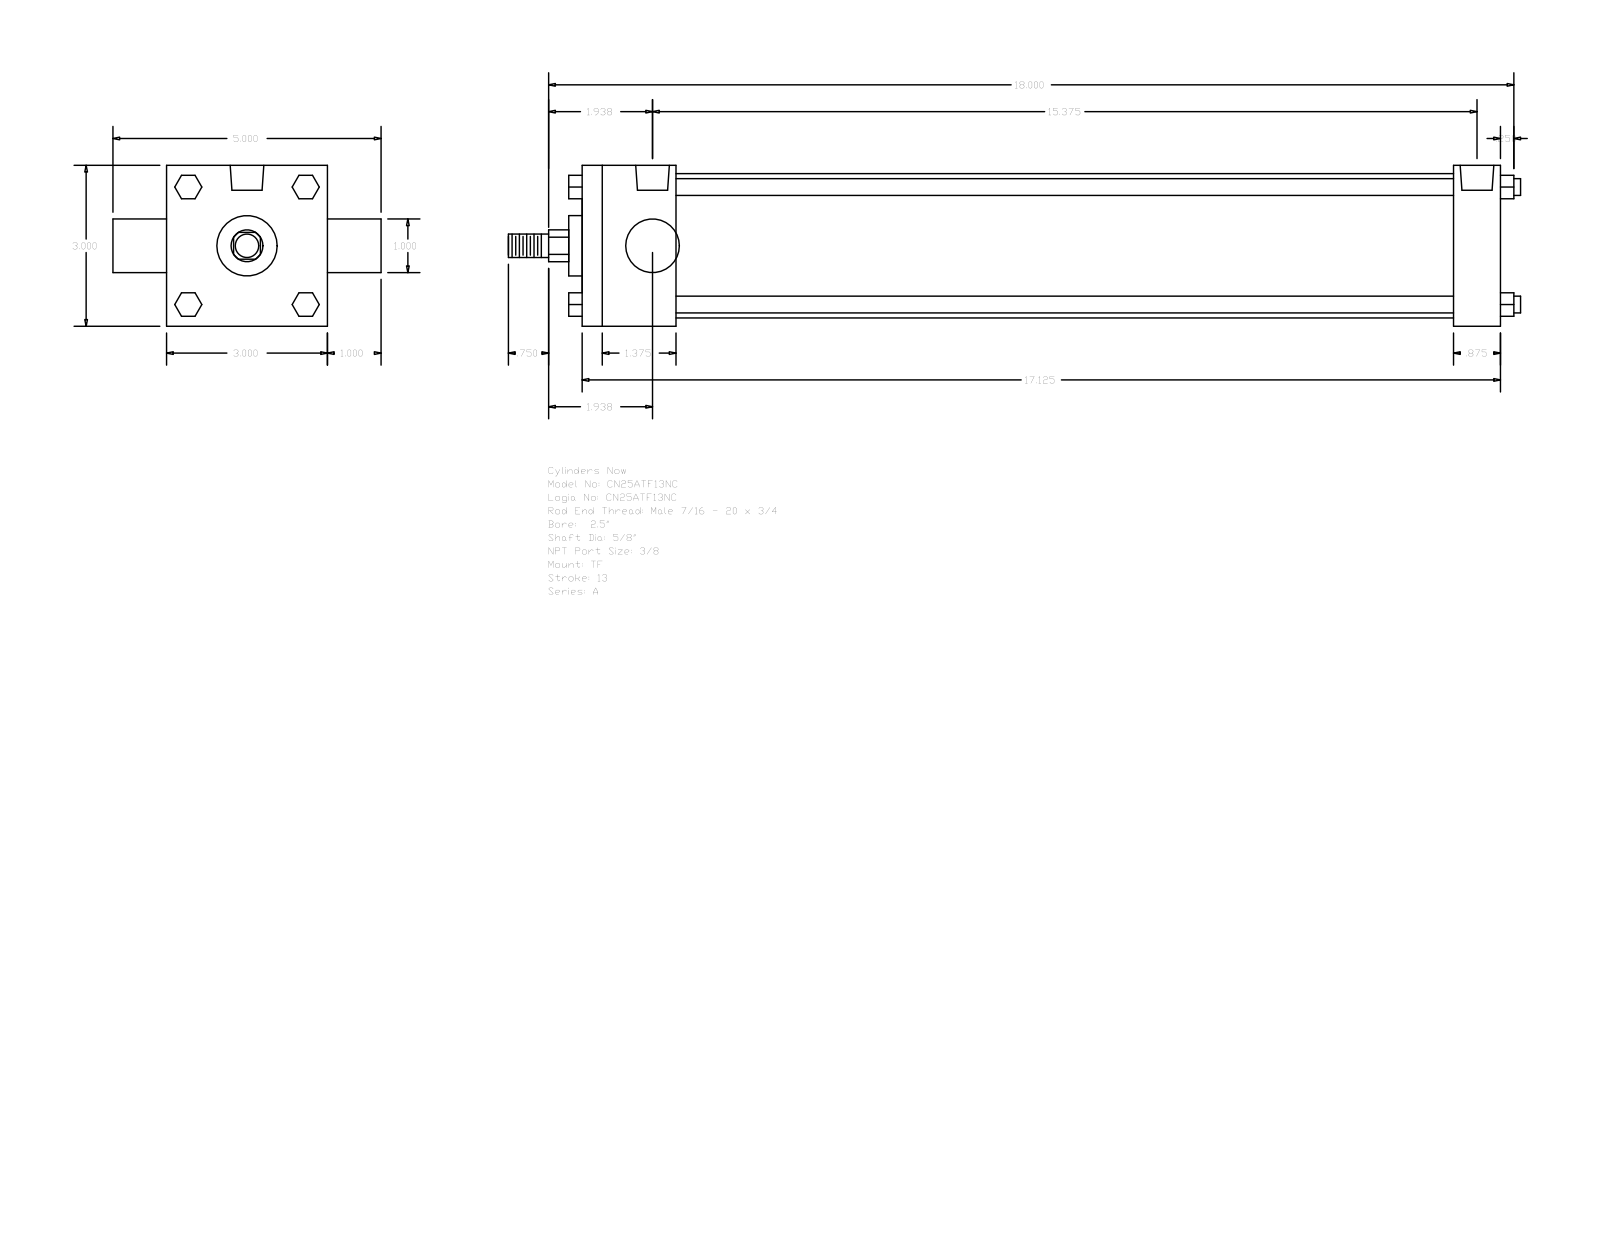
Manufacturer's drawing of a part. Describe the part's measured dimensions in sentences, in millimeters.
The part is named "A_TF__0250_0.625". Its 3-D file was written by "GSSL Pune (CONFIG_CONTROL_DESIGN)". It is 0 solids with 120 faces: 92 planar, 28 cylindrical and 0 other. Overall it measures 479.43 by 127 by 76.2 millimeters. Round holes: 3 of diameter 5.56, 2 of diameter 15.93. Round bosses or shafts: 4 of diameter 7.94, 1 of diameter 68.33, 1 of diameter 28.57, 1 of diameter 25.4, 1 of diameter 15.88, 1 of diameter 11.11. Partial cylindrical surfaces (rounded edges, fillets, slot ends): 1 of radius 7.54. The main face-to-face distances are 76.2, 434.97, 44.45, 412.74, 368.29, 390.52, 22.23, 25.4, 101.6, 6.35. The hole center spacings are 2.38, 392.91, 390.53, 395.29.
